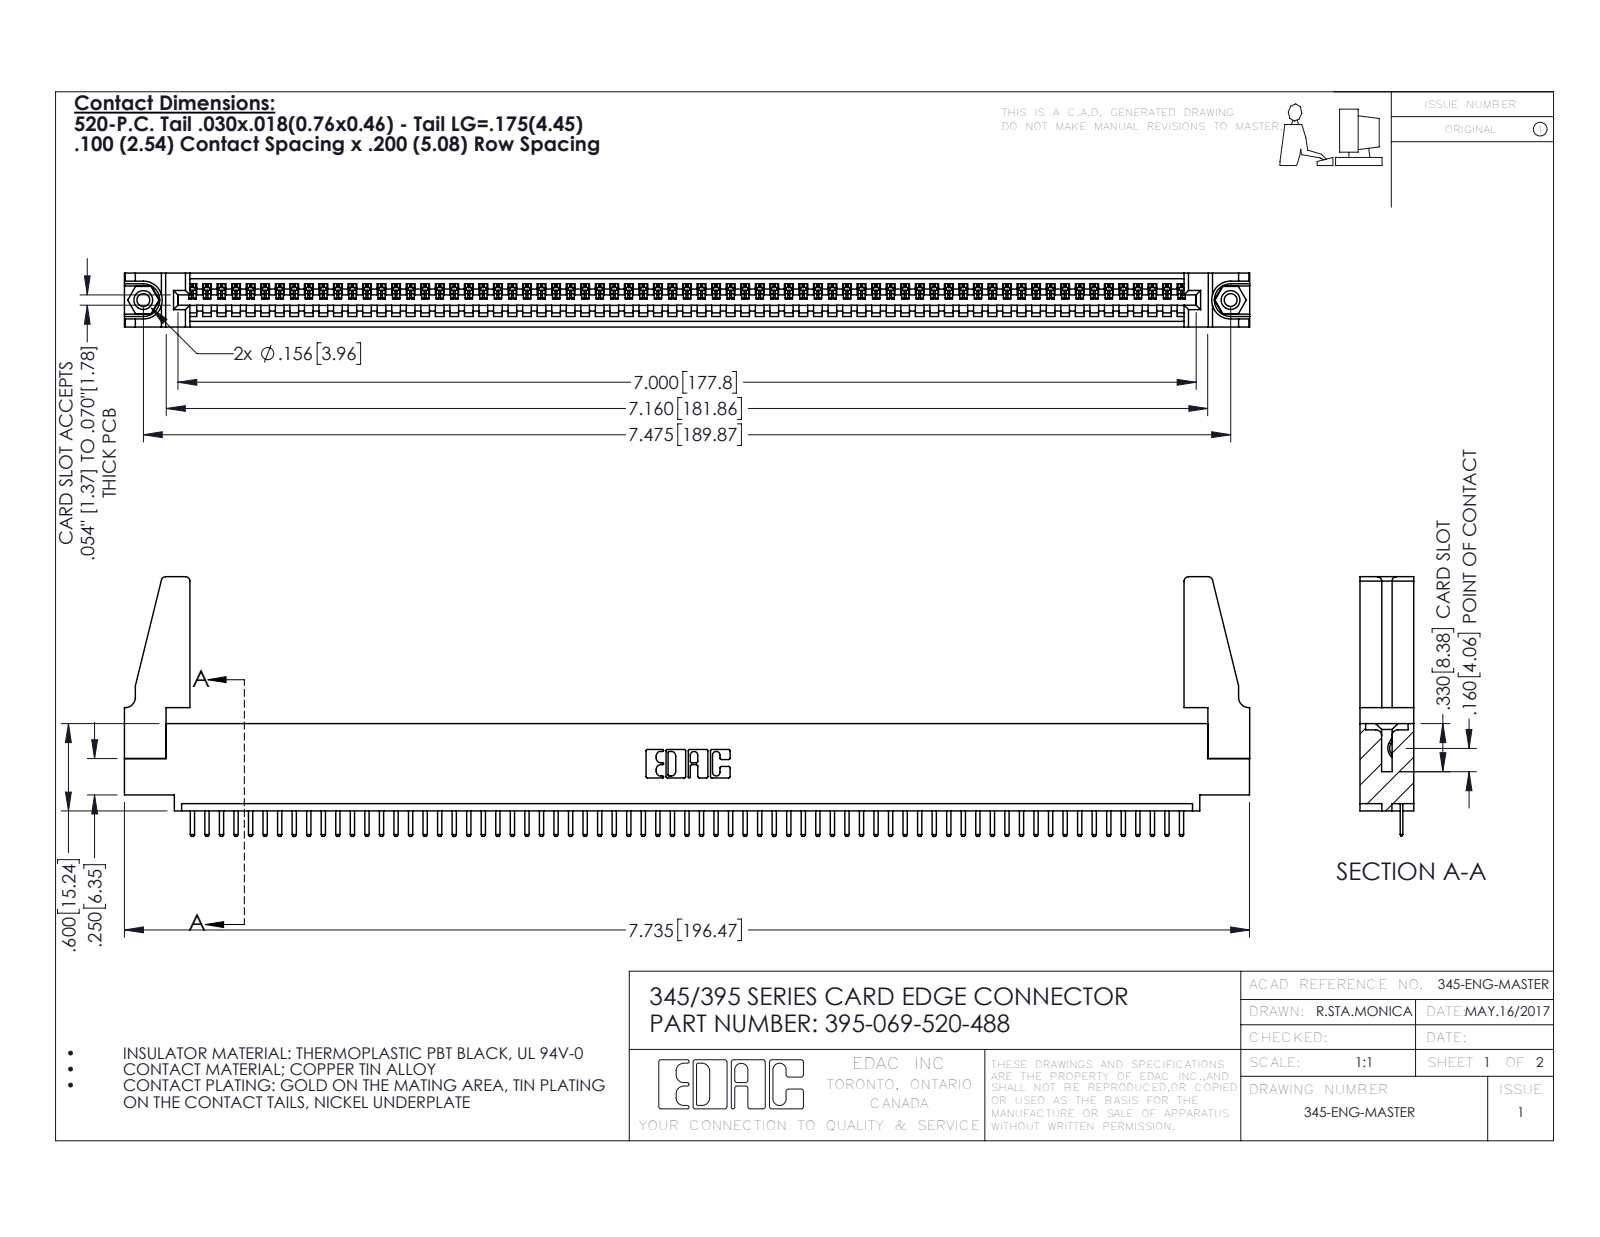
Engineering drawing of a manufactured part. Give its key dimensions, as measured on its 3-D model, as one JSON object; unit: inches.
{"part_name": "395-069-520-488; 345-250-001_345-250-001-102; 345-220-078_345-220-088; 345 Part_0.110 Offset - 0.156 Dia-TH (+1 more)", "step_written_by": "SolidWorks 2016 (CONFIG_CONTROL_DESIGN)", "units": "inches", "bodies": {"solids": 74, "faces": 4532, "planar": 3054, "cylindrical": 1462, "other": 16}, "overall_size": [7.736, 1.785, 0.37], "volume_in3": 1.334, "surface_area_in2": 42.88, "round_holes": [[0.089, 2], [0.125, 2], [0.156, 2], [0.064, 1]], "round_bosses_or_shafts": [[0.155, 2]], "partial_cylinders_radius": [[0.01, 140], [0.006, 138], [0.01, 22], [0.03, 8], [0.007, 6], [0.031, 6], [0.026, 3], [0.031, 2]], "face_to_face_distances": [0.072, 0.298, 0.37, 0.098, 0.272, 0.025, 0.2, 0.225, 0.072, 0.149], "hole_center_spacings": [0.27, 7.239, 7.475]}
